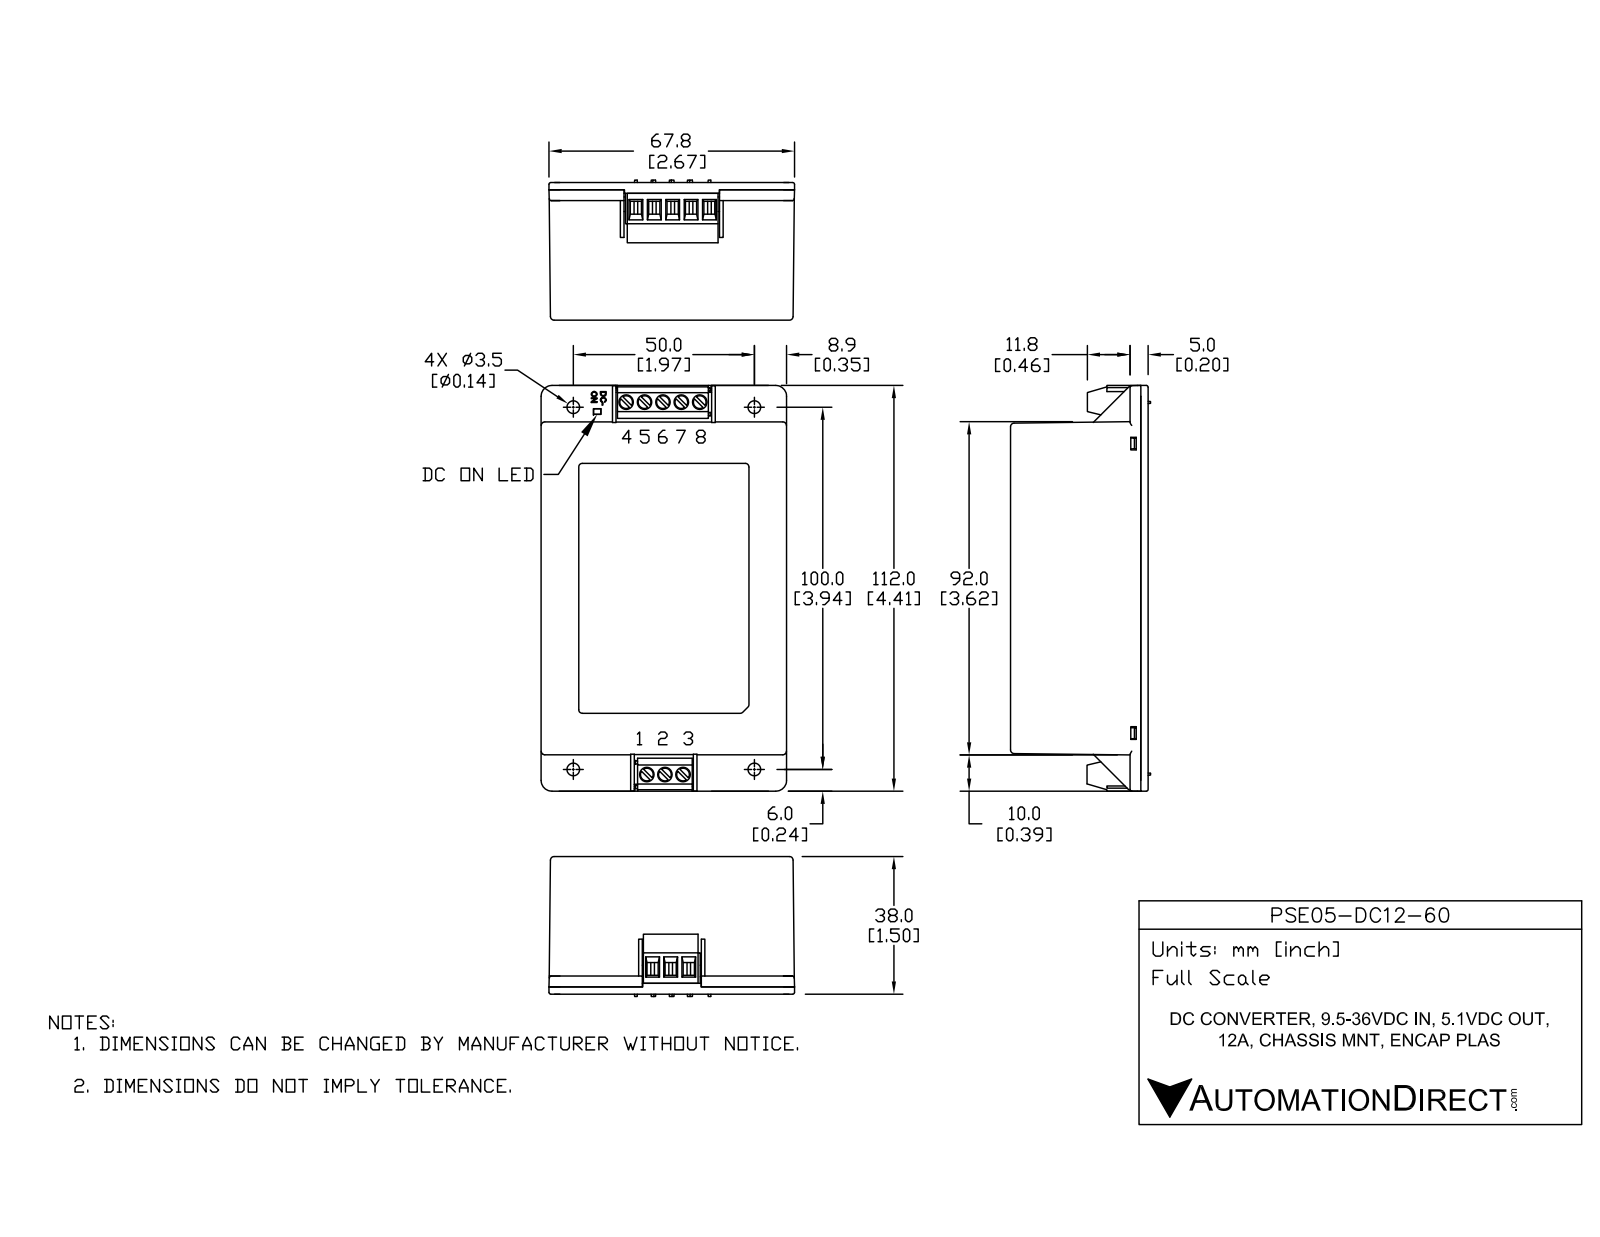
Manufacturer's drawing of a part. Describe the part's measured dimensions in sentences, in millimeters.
The part is named "PSE05-DC12-60". Its 3-D file was written by "SolidWorks 2015 (AUTOMOTIVE_DESIGN)". It is 0 solids with 390 faces: 282 planar, 89 cylindrical and 19 other. Overall it measures 112.92 by 69.3 by 37.06 millimeters. Round holes: 10 of diameter 4, 4 of diameter 3.5, 1 of diameter 2.46, 1 of diameter 4.08, 1 of diameter 6.5. Round bosses or shafts: 4 of diameter 1.5, 1 of diameter 5. Partial cylindrical surfaces (rounded edges, fillets, slot ends): 17 of radius 1, 8 of radius 0.5, 4 of radius 2.15, 4 of radius 2.65, 4 of radius 3, 3 of radius 3.25. The main face-to-face distances are 1, 0.98, 35, 34, 0.7, 1.02, 1.7, 33.3, 34.99, 33.99. The hole center spacings are 5.08, 10.16, 50, 102.13, 102.29, 5, 15.24, 100.
